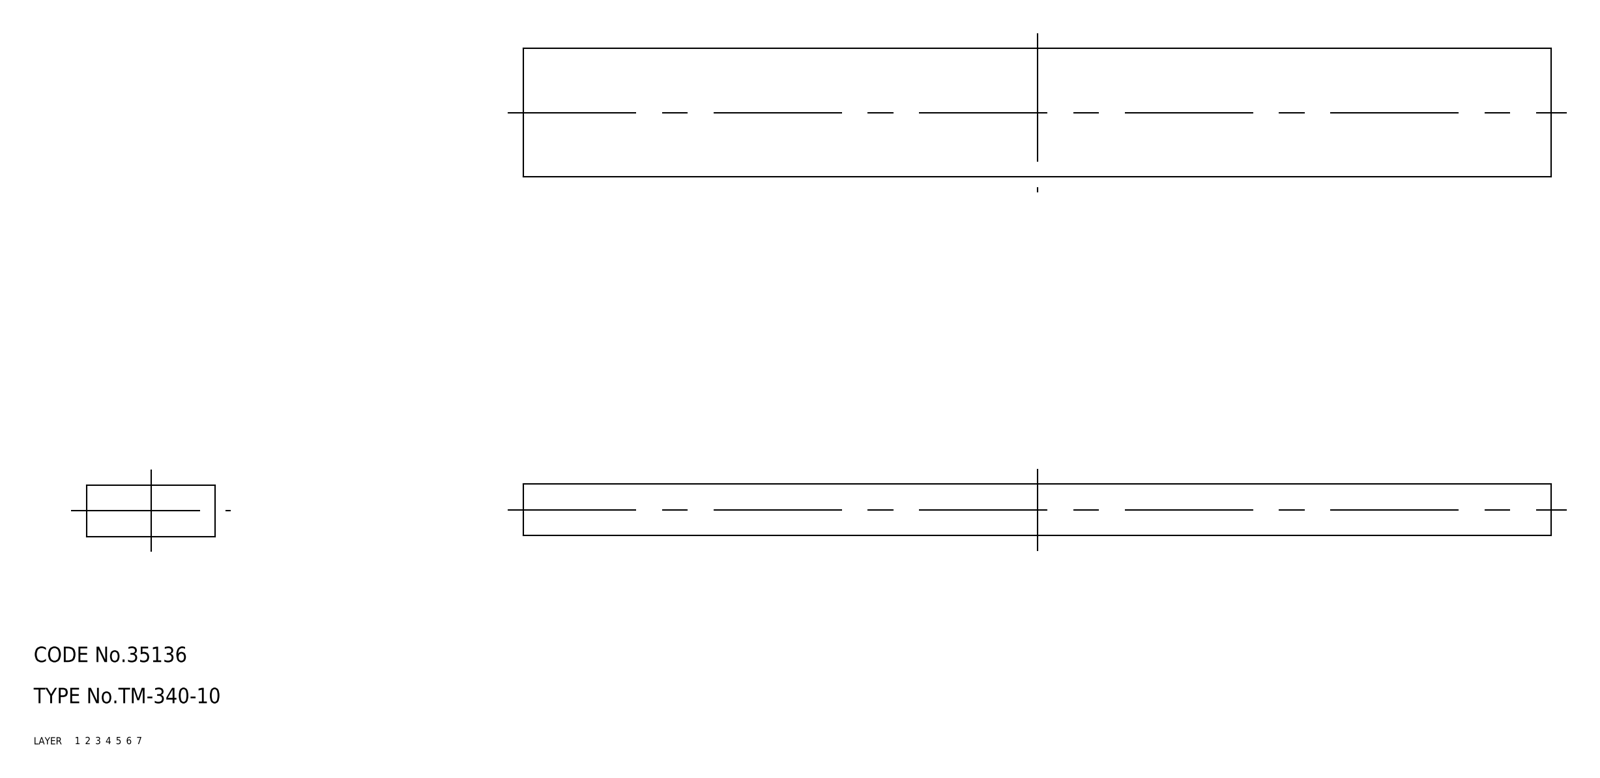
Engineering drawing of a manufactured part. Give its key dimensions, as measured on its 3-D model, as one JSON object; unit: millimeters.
{"part_name": "rubber foam; TM_340_10", "step_written_by": "SolidWorks 2015 (AUTOMOTIVE_DESIGN)", "units": "millimeters", "bodies": {"solids": 1, "faces": 6, "planar": 6, "cylindrical": 0, "other": 0}, "overall_size": [200, 25, 10], "volume_mm3": 50000, "surface_area_mm2": 14500, "face_to_face_distances": [10, 25, 200]}
